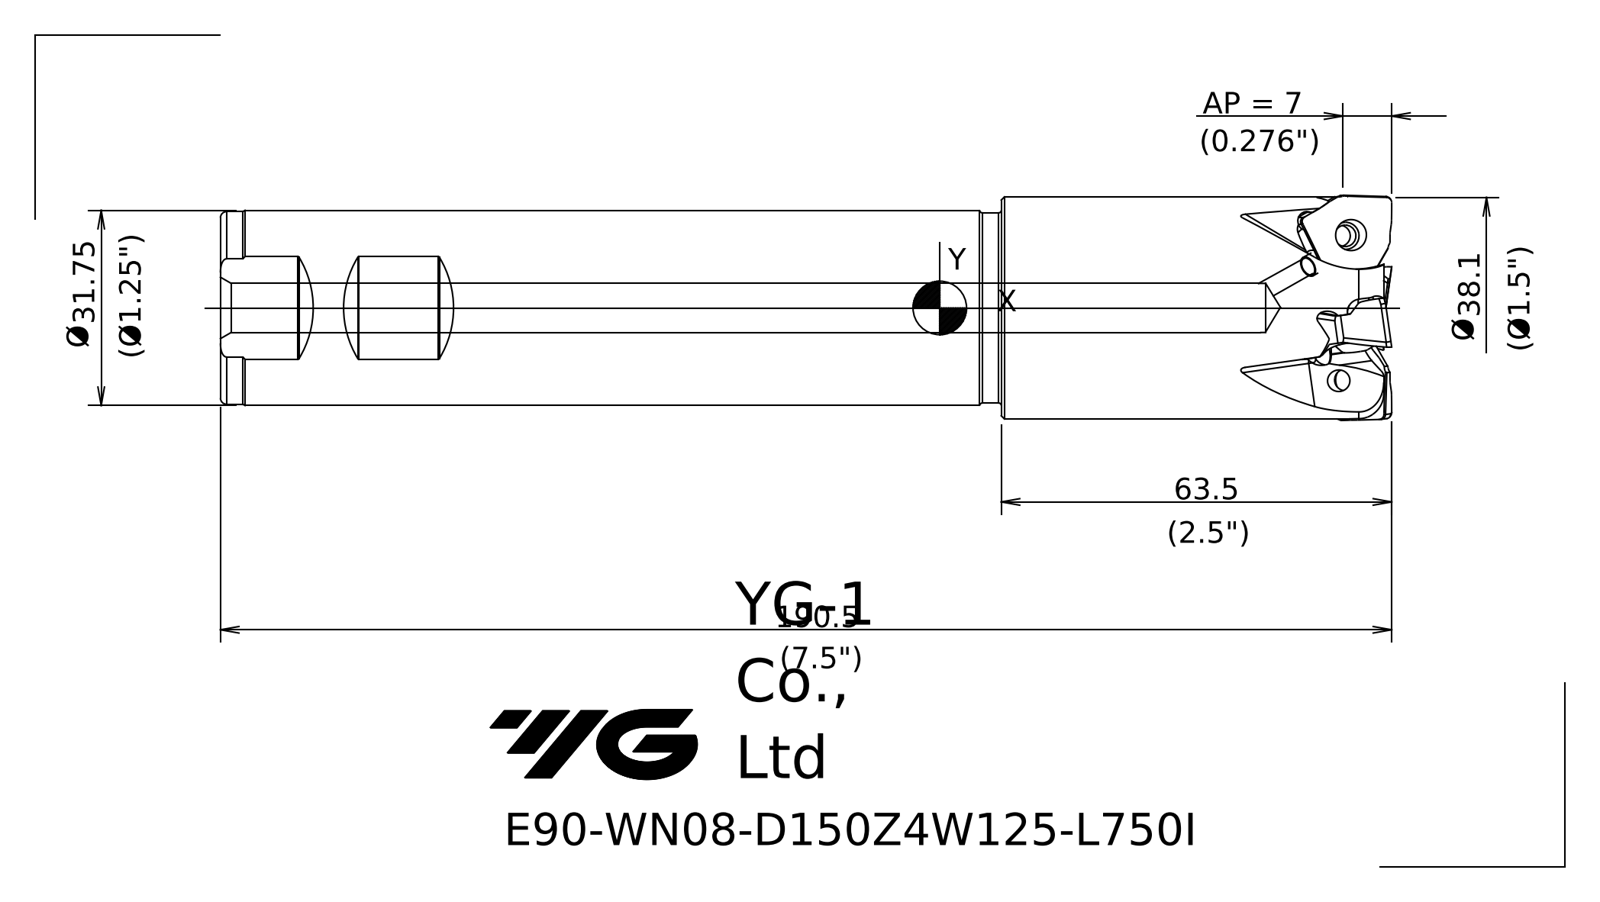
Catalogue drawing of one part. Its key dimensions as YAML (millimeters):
part_name: "10223F5CCA8Abc35"
step_written_by: "SIEMENS PLM Software NX 10.0 (AP203_CONFIGURATION_CONTROLLED_3D_DESIGN_OF_MECHANICAL_PARTS_AND_ASSEMBLIES_MIM_LF)"
units: millimeters
bodies: {solids: 1, faces: 68, planar: 9, cylindrical: 8, other: 51}
overall_size: [190.5, 38.1, 38.1]
volume: 153134
surface_area: 29555
round_holes:
  - {diameter: 8, count: 1}
round_bosses_or_shafts:
  - {diameter: 36.1, count: 1}
  - {diameter: 31.75, count: 1}
  - {diameter: 31.35, count: 1}
  - {diameter: 30.95, count: 1}
partial_cylinders:
  - {radius: 0.3, count: 3}
face_to_face_distances: [127, 62.2, 189.2, 4.2, 58, 185, 16.14]
